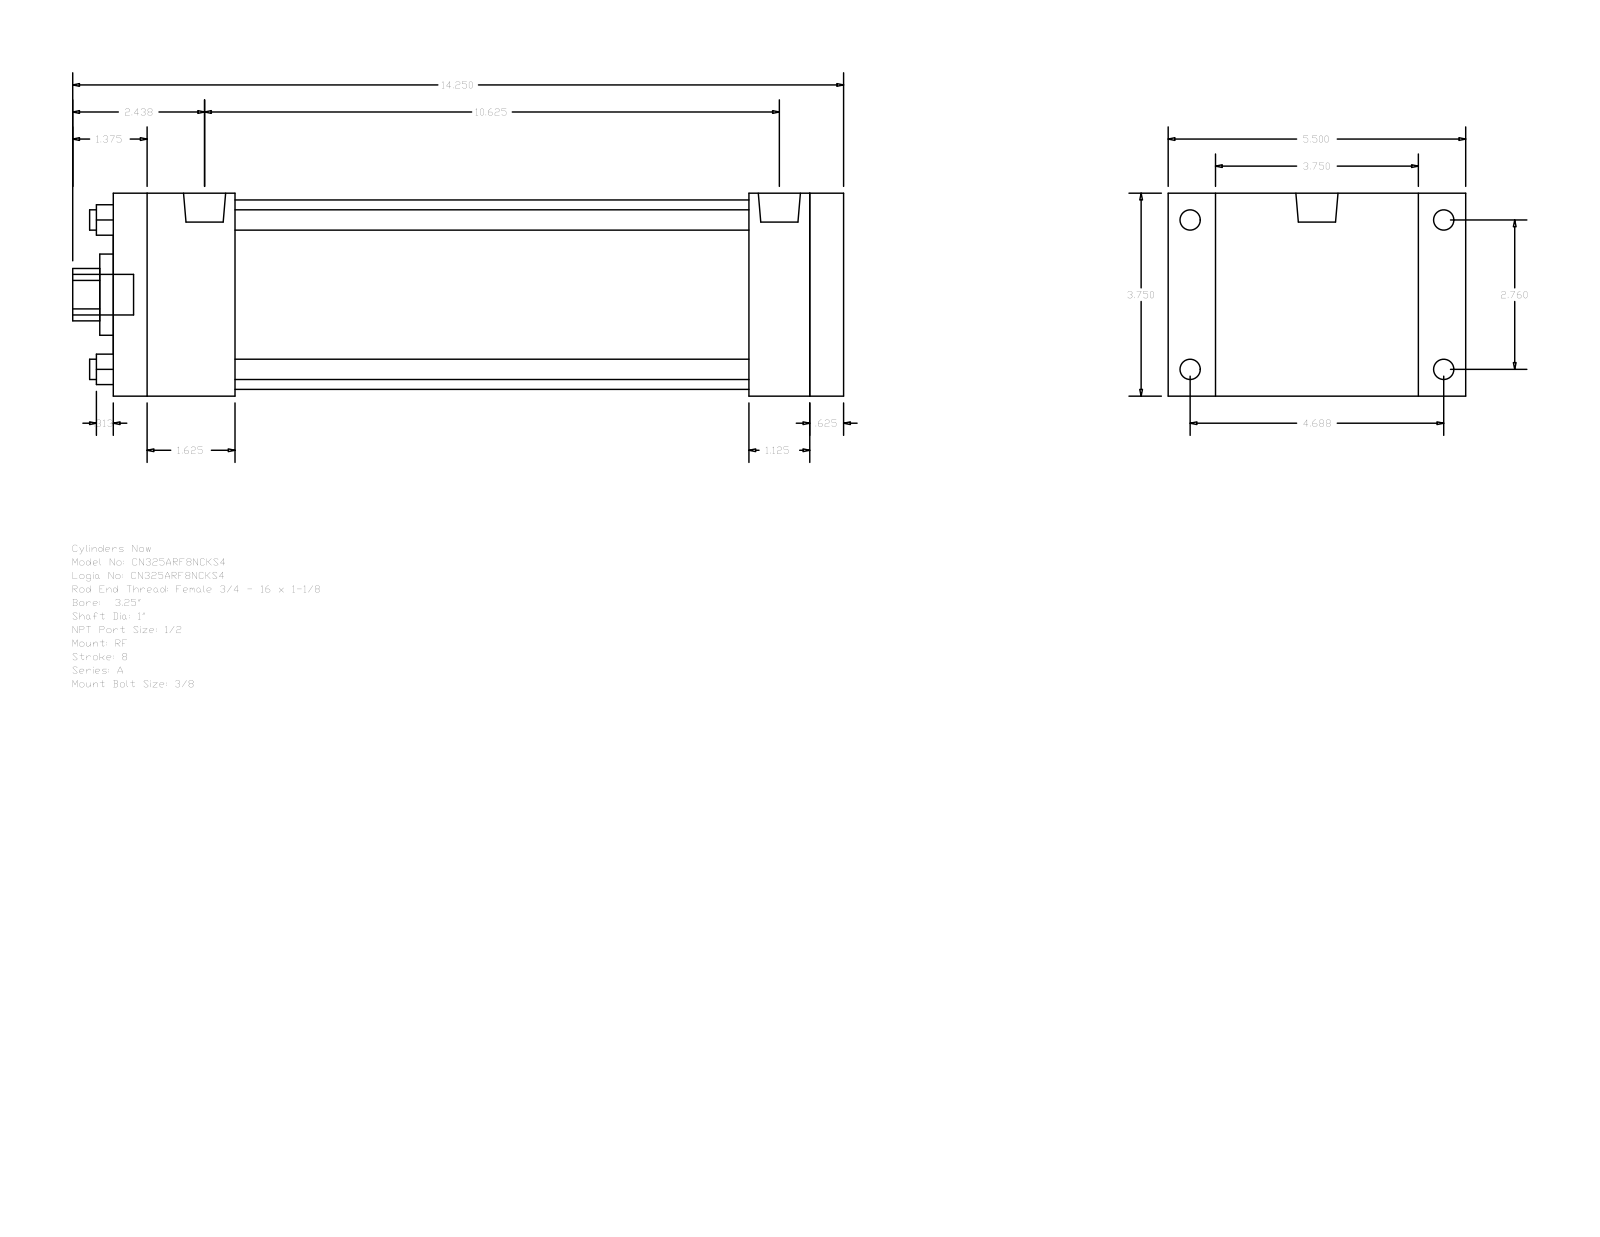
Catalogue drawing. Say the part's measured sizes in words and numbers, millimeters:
The part is named "A_RF__0325_1". Its 3-D file was written by "GSSL Pune (CONFIG_CONTROL_DESIGN)". It is 0 solids with 92 faces: 64 planar, 28 cylindrical and 0 other. Overall it measures 361.95 by 139.7 by 95.25 millimeters. Round holes: 4 of diameter 9.53, 1 of diameter 25.4, 1 of diameter 38.1, 1 of diameter 88.9. Round bosses or shafts: 4 of diameter 9.53, 4 of diameter 8.73, 2 of diameter 19.77, 1 of diameter 19.05. Partial cylindrical surfaces (rounded edges, fillets, slot ends): 1 of radius 12.29. The main face-to-face distances are 95.24, 342.9, 327.02, 15.88, 22.23, 117.47, 28.57, 298.45, 44.45, 57.15. The hole center spacings are 49.57, 70.1, 99.14.
